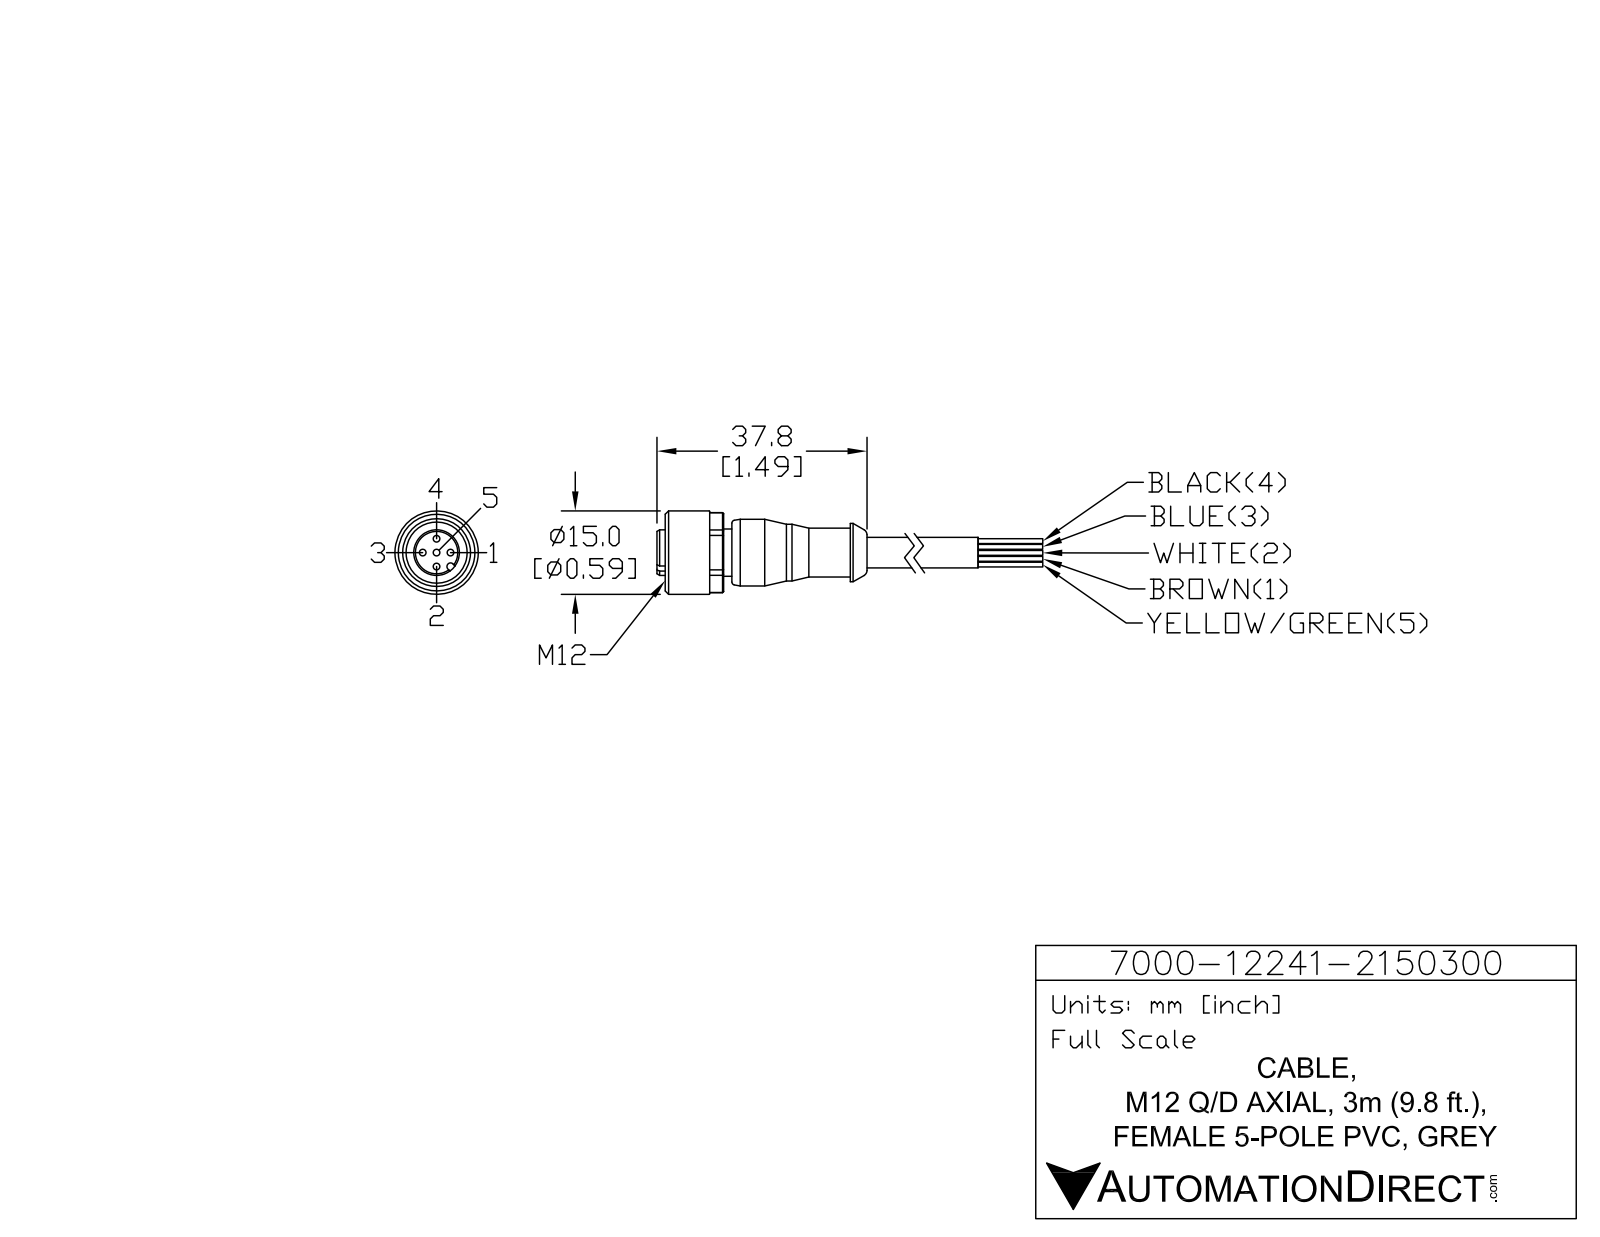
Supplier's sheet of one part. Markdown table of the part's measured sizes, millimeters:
| quantity | value |
| --- | --- |
| part name | 7000-12241-2150300 |
| STEP written by | SolidWorks 2015 (AUTOMOTIVE_DESIGN) |
| units | millimeters |
| bodies | 1 solid, 93 faces (29 planar, 36 cylindrical, 28 other) |
| overall size | 57.8 × 15 × 15 |
| volume | 4 024 mm³ |
| surface area | 2 667 mm² |
| round holes (diameter × count) | 1.2 × 5, 11 × 1 |
| round bosses / shafts (diameter × count) | 15 × 1, 12 × 1, 10.5 × 1, 10.2 × 1, 8.8 × 1, 8.5 × 1, 8.2 × 1, 5.5 × 1 |
| partial cylindrical surfaces (radius × count) | 0.65 × 1, 7.2 × 1 |
| main face-to-face distances | 12, 1.5, 3, 13, 9, 25.8, 7.5, 10.5, 2.5, 13.5 |
| hole center spacings | 2.5, 3.54, 5 |
